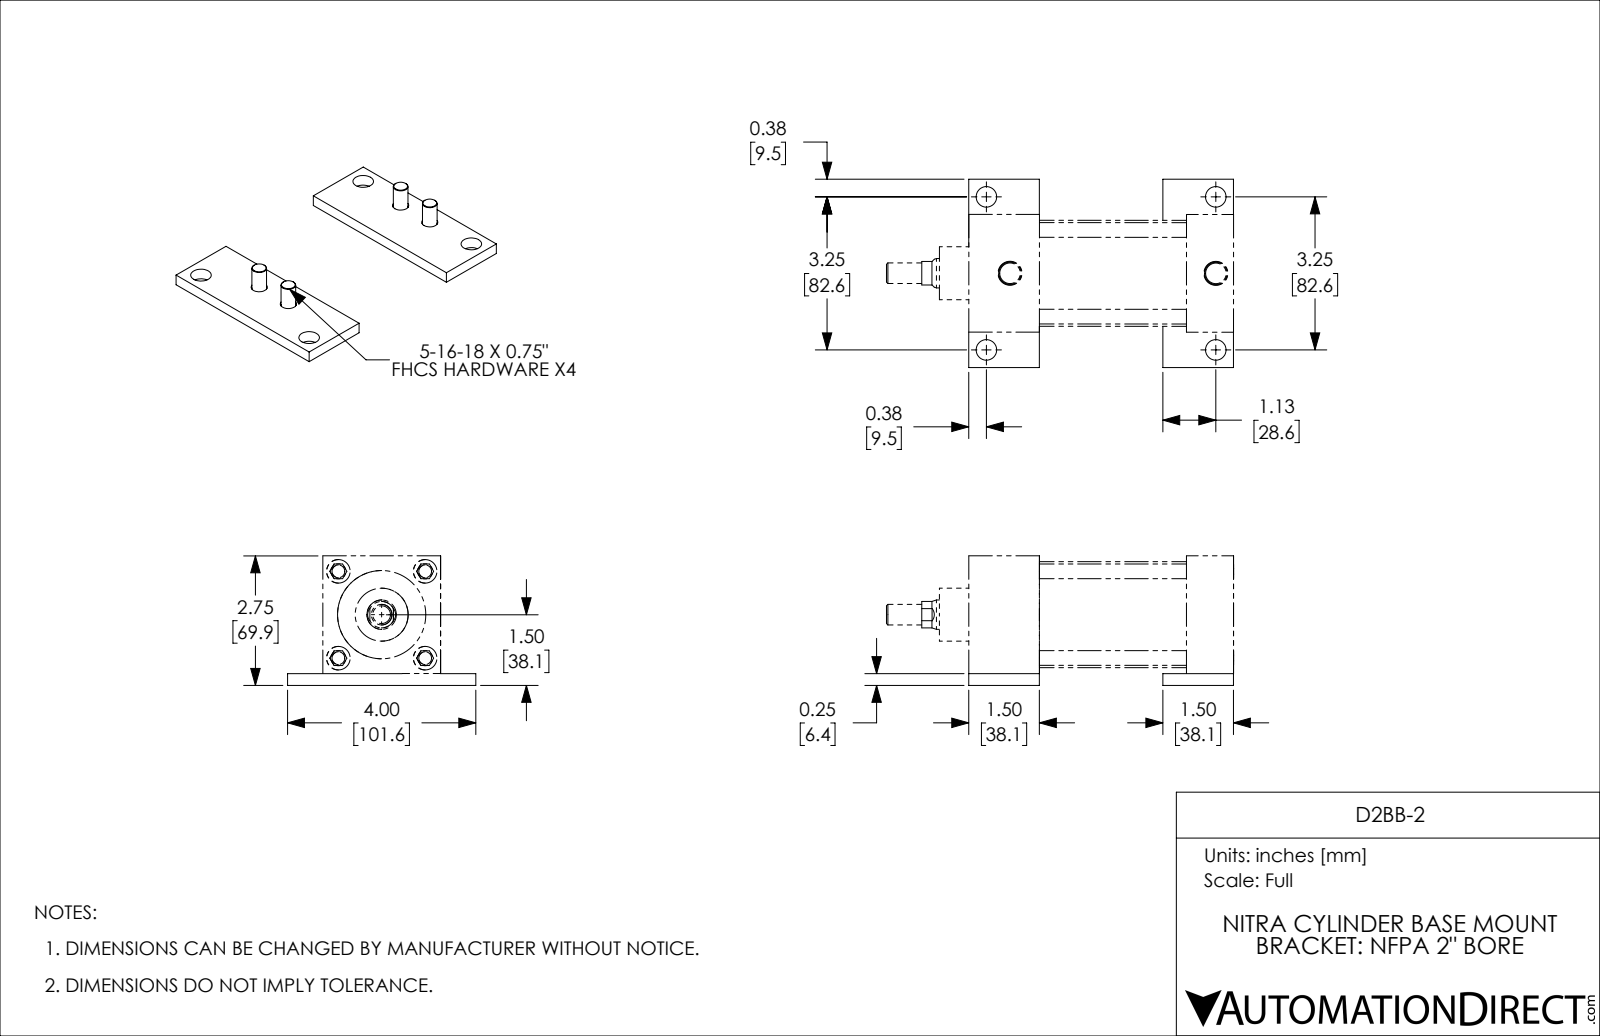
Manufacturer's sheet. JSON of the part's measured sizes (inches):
{"part_name": "D2BB-2; D2BB-2_1; D2BB-2_2", "step_written_by": "SolidWorks 2019 (CONFIG_CONTROL_DESIGN)", "units": "inches", "bodies": {"solids": 6, "faces": 236, "planar": 48, "cylindrical": 100, "other": 88}, "overall_size": [5.624, 4, 0.75], "volume_in3": 2.958, "surface_area_in2": 36.51, "round_holes": [[0.343, 4], [0.437, 4]], "round_bosses_or_shafts": [[0.656, 4], [0.313, 4]], "face_to_face_distances": [0.25, 1.5, 4.124, 5.624, 2.624, 4, 0.75, 0.5, 0.139, 0.111], "hole_center_spacings": [0.875, 3.25, 4.25, 4.875, 5.859, 1.188, 1.189, 1.313]}
